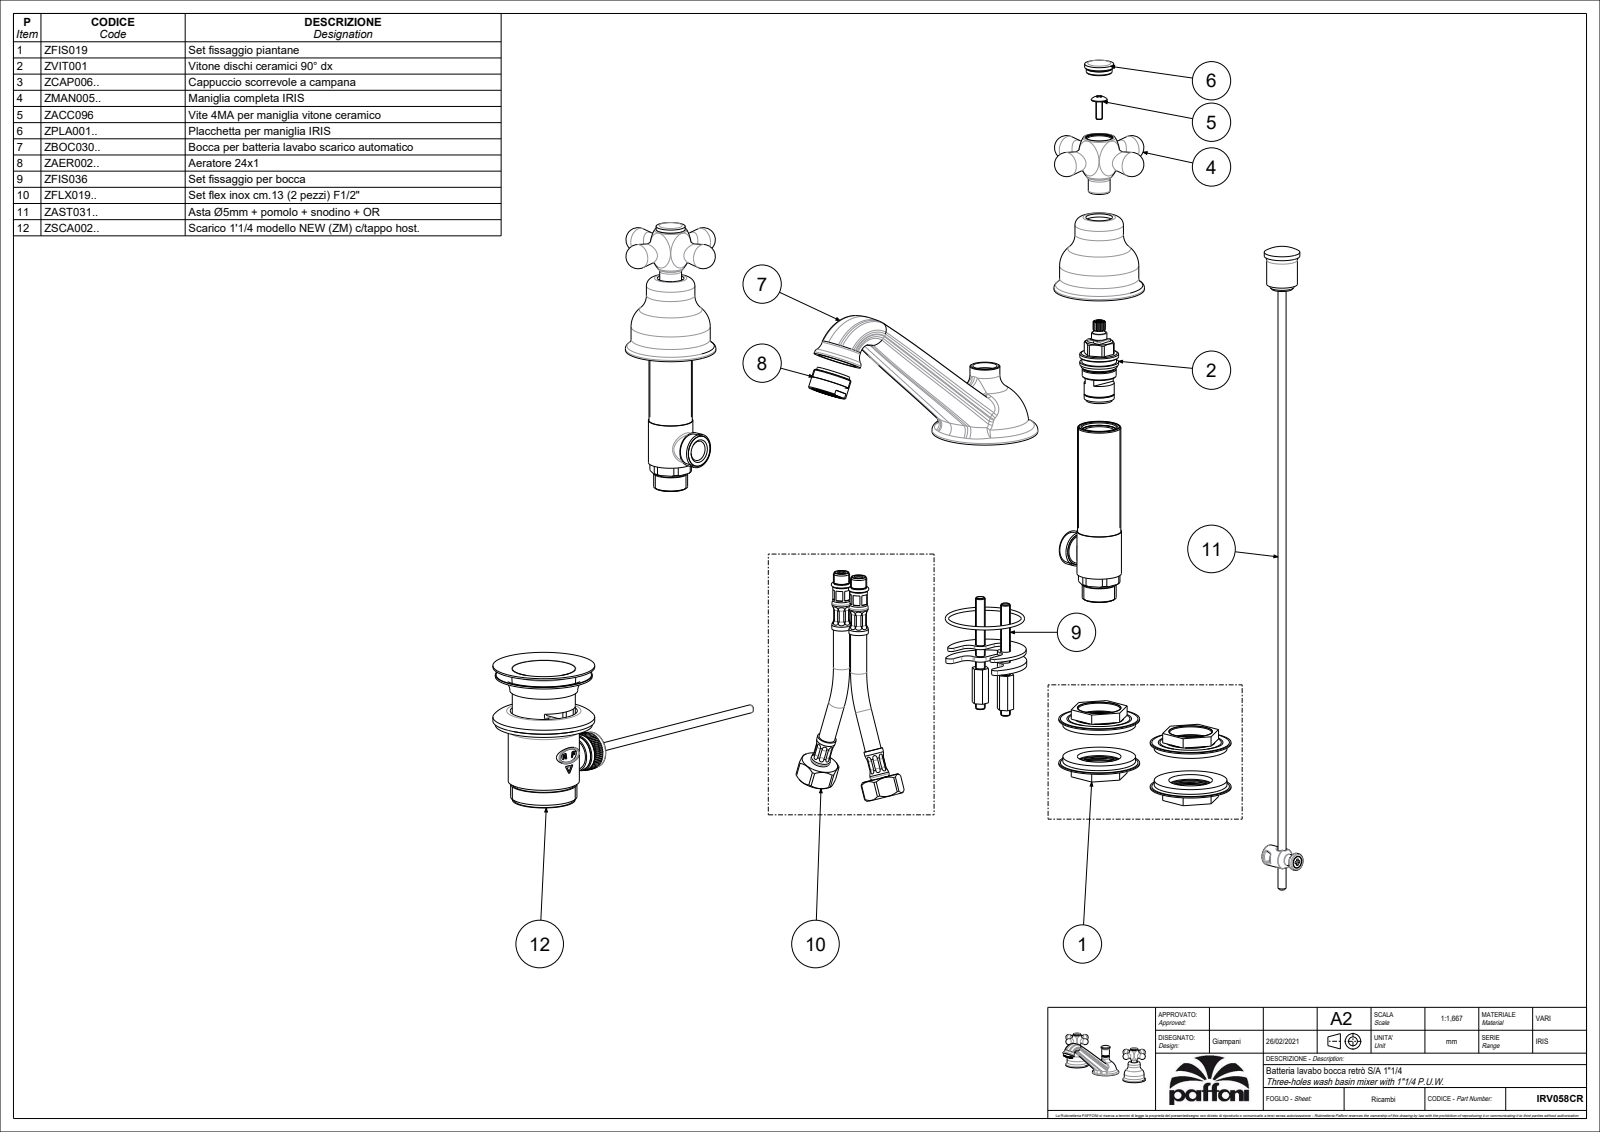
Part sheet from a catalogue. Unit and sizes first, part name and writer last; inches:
Units: inches
Overall size (bounding box): 10.709 × 7.043 × 3.719
Round holes (diameter × count): ⌀0.433 ×3, ⌀0.177 ×2, ⌀0.346 ×2, ⌀0.354 ×2, ⌀0.406 ×2, ⌀0.638 ×2, ⌀0.642 ×2, ⌀0.748 ×2, ⌀1.012 ×2, ⌀1.063 ×2, ⌀1.772 ×2, ⌀2.079 ×2
Round bosses / shafts (diameter × count): ⌀0.945 ×3, ⌀2.165 ×2, ⌀1.929 ×2, ⌀1.161 ×2, ⌀1.102 ×2, ⌀1.055 ×2, ⌀0.843 ×2, ⌀0.732 ×2
Partial cylindrical surfaces — rounded edges, fillets, slot ends (radius × count): R0.004 ×34, R0.02 ×4, R0.039 ×4, R0.197 ×2, R0.295 ×2, R0.357 ×2, R0.37 ×2, R0.296 ×1
Main face-to-face distances: 0.15, 0.098, 0.051, 0.118, 0.031, 0.067, 0.02, 0.071, 0.047, 0.028
Hole centre spacings: 0.432, 3.656, 3.937, 4.244, 0.591, 7.874
Volume: 11.71 in³ · Surface area: 172.7 in²
Bodies: 9 solids, 2218 faces (1556 planar, 244 cylindrical, 418 other)
Part name (STEP PRODUCT): IRV058CR
STEP written by: CREO PARAMETRIC BY PTC INC, 2020044 (CONFIG_CONTROL_DESIGN)
